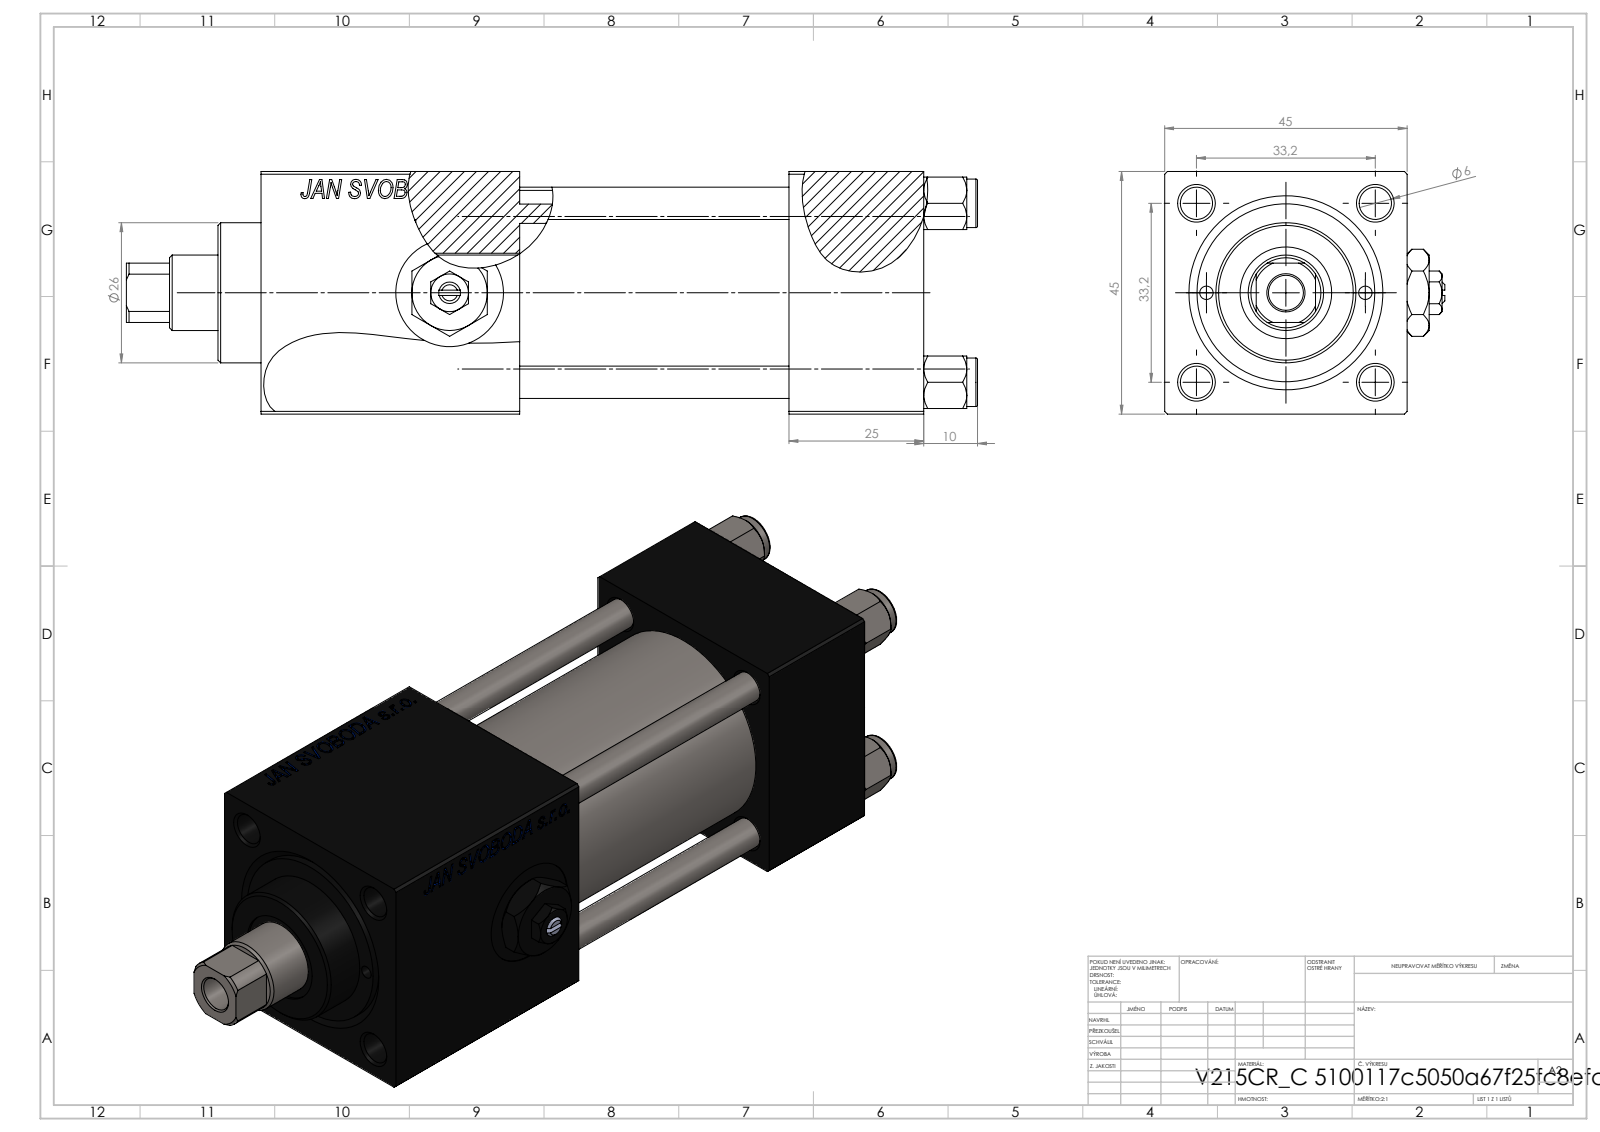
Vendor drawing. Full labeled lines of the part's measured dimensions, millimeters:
Part name (STEP PRODUCT): V215CR_VCP_C; Zatka_pro_OIL_PORT; V215_VC_A; V215CR_C_Body (+2 more)
STEP written by: SolidWorks 2019 (CONFIG_CONTROL_DESIGN)
Units: millimetres
Bodies: 12 solids, 1201 faces (551 planar, 94 cylindrical, 556 other)
Overall size (bounding box): 158 × 52 × 45
Volume: 193 143 mm³ · Surface area: 67 925 mm²
Round holes (diameter × count): ⌀6 ×4, ⌀2.5 ×2, ⌀7 ×2, ⌀13.16 ×2, ⌀20 ×2, ⌀6.5 ×1, ⌀14 ×1, ⌀17 ×1, ⌀24 ×1, ⌀32 ×1, ⌀33 ×1
Round bosses / shafts (diameter × count): ⌀9 ×4, ⌀38 ×1, ⌀26 ×1
Partial cylindrical surfaces — rounded edges, fillets, slot ends (radius × count): R6.5 ×1
Main face-to-face distances: 45, 25, 98, 123, 50, 75, 48, 94.3, 69.3, 19.3
Hole centre spacings: 16.7, 23.48, 33.2, 35.47, 14.75, 46.95, 29.5, 75.5
